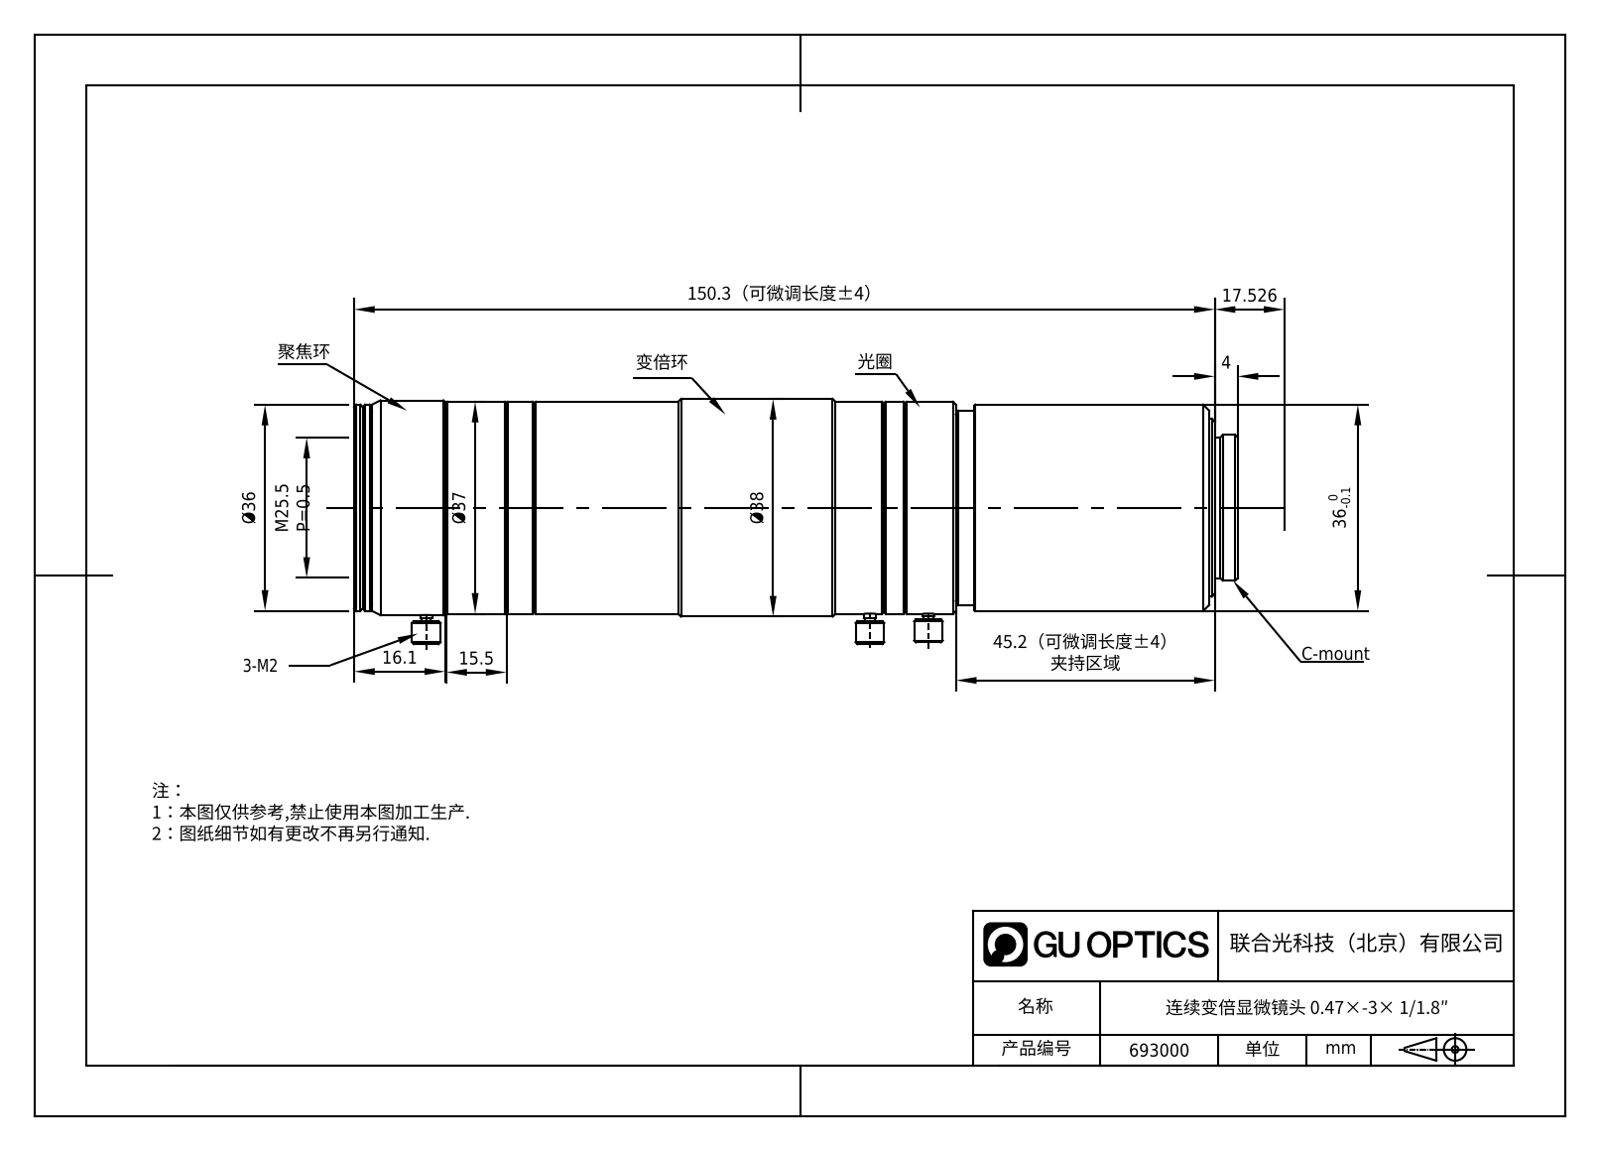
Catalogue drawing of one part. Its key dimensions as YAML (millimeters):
part_name: "VSZ-0530"
step_written_by: "SolidWorks 2016 (CONFIG_CONTROL_DESIGN)"
units: millimeters
bodies: {solids: 1, faces: 274, planar: 42, cylindrical: 82, other: 150}
overall_size: [154.29, 42.8, 38]
volume: 141349
surface_area: 28292
round_holes:
  - {diameter: 9, count: 1}
  - {diameter: 20, count: 1}
  - {diameter: 22, count: 1}
  - {diameter: 24.5, count: 1}
  - {diameter: 25, count: 1}
  - {diameter: 25.5, count: 1}
  - {diameter: 27.5, count: 1}
  - {diameter: 28, count: 1}
  - {diameter: 30, count: 1}
  - {diameter: 33.5, count: 1}
  - {diameter: 34, count: 1}
round_bosses_or_shafts:
  - {diameter: 5, count: 3}
  - {diameter: 2, count: 3}
  - {diameter: 1.6, count: 3}
  - {diameter: 38, count: 1}
  - {diameter: 37.5, count: 1}
  - {diameter: 37, count: 1}
  - {diameter: 36, count: 1}
  - {diameter: 35, count: 1}
face_to_face_distances: [9, 45.19, 112.4, 148.09, 35.69, 139.09, 26.69, 136.1, 23.7, 2.99]
